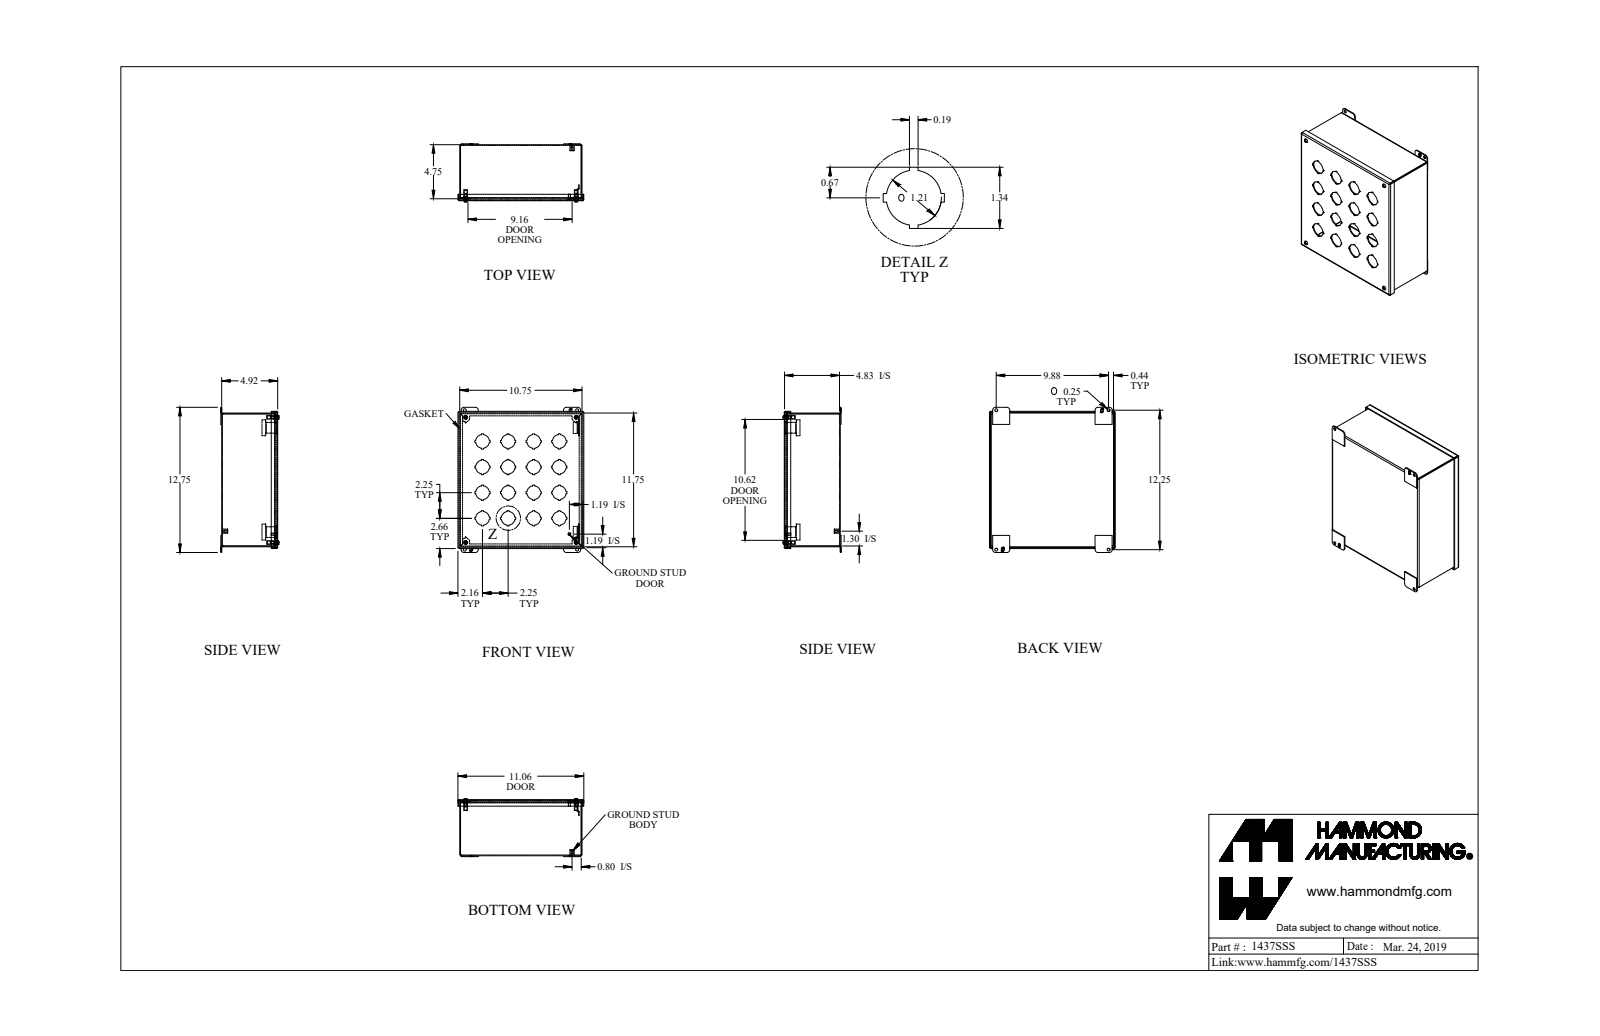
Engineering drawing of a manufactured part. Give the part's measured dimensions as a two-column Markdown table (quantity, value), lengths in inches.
| quantity | value |
| --- | --- |
| part name | 1437SSS_Default |
| STEP written by | SolidWorks 2019 (CONFIG_CONTROL_DESIGN) |
| units | inches |
| bodies | 23 solids, 861 faces (615 planar, 216 cylindrical, 30 other) |
| overall size | 12.75 × 11.06 × 5.104 |
| volume | 39.58 in³ |
| surface area | 1 061 in² |
| round holes (diameter × count) | 1.21 × 16, 0.25 × 8, 0.065 × 4, 0.239 × 4, 0.253 × 4, 0.406 × 4, 0.156 × 1 |
| round bosses / shafts (diameter × count) | 0.19 × 5, 0.406 × 4, 0.315 × 4, 0.148 × 4, 0.375 × 1, 0.25 × 1 |
| partial cylindrical surfaces (radius × count) | 0.036 × 12, 0.108 × 12, 0.25 × 8, 0.029 × 4, 0.086 × 4, 0.171 × 4 |
| main face-to-face distances | 0.072, 4.85, 4.922, 4.778, 10.678, 0.072, 11.678, 10.606, 10.75, 11.75 |
| hole center spacings | 2.25, 5.031, 3.182, 4.5, 9.71, 9.711, 9.813, 10.999 |
